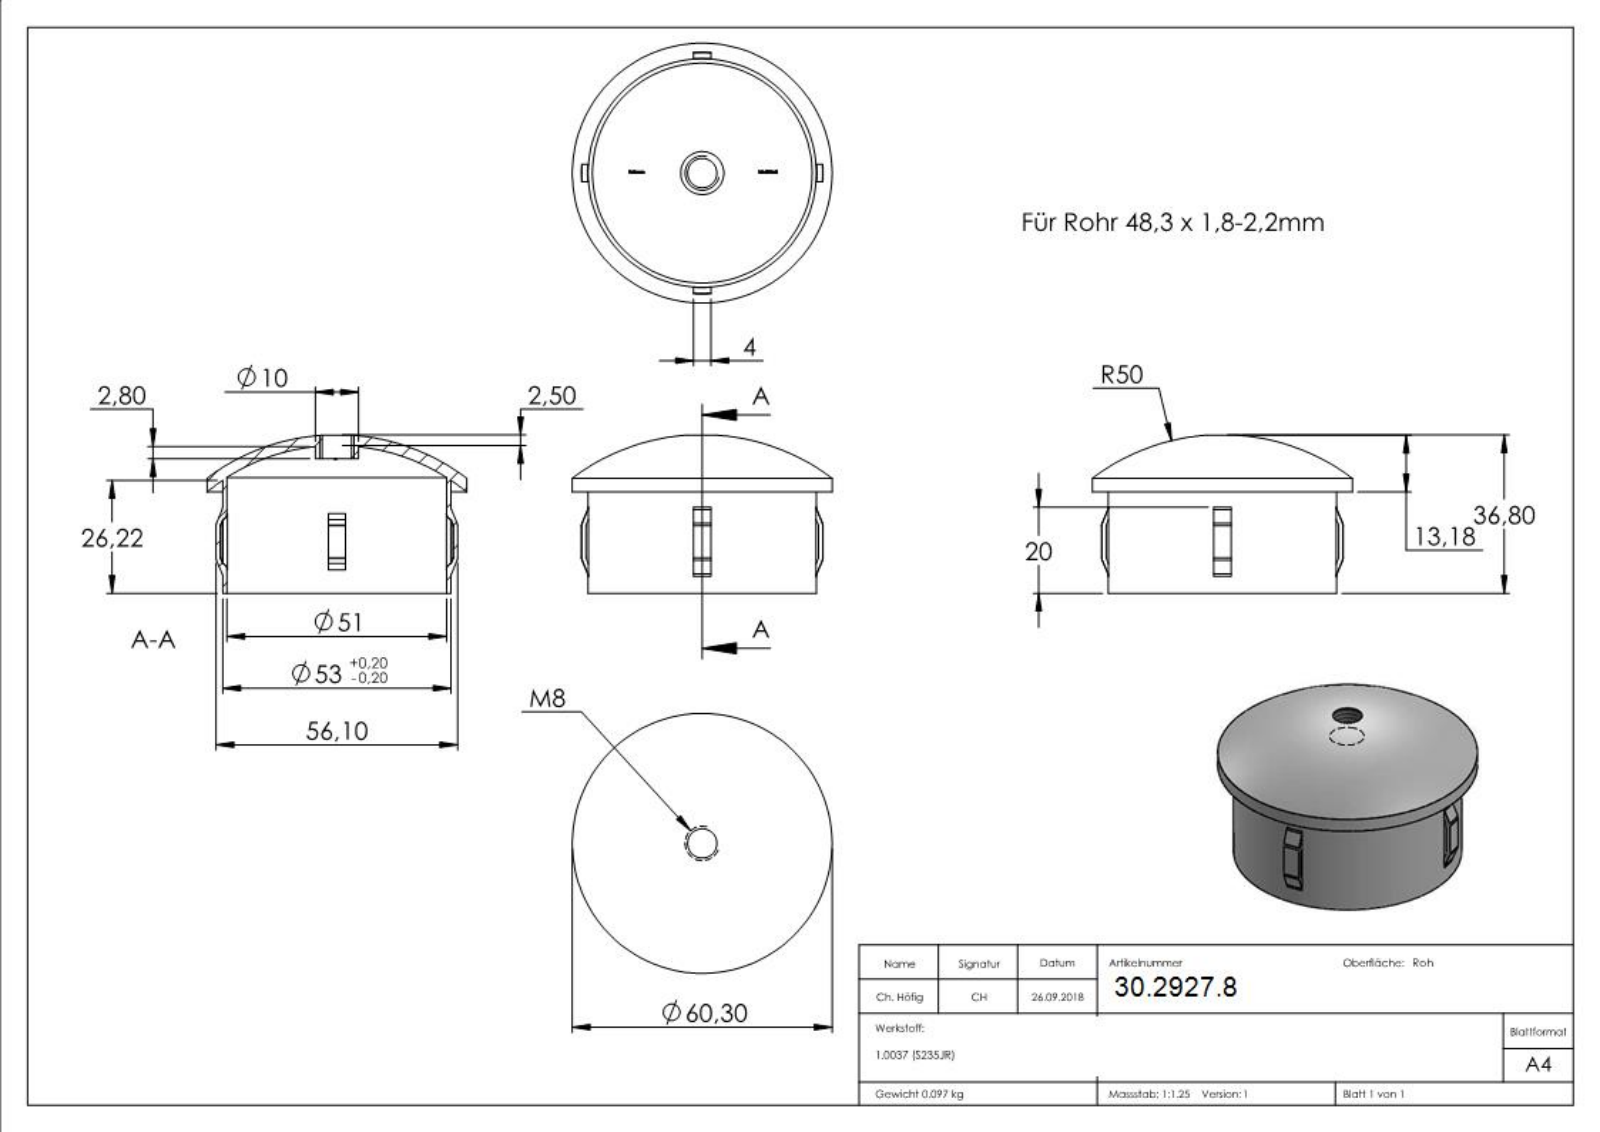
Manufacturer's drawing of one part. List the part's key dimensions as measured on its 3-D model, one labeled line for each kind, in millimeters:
Part name (STEP PRODUCT): 166-6001-M8
STEP written by: SolidWorks 2015 (CONFIG_CONTROL_DESIGN)
Units: millimetres
Bodies: 1 solid, 358 faces (114 planar, 20 cylindrical, 224 other)
Overall size (bounding box): 60.3 × 60.3 × 36.61
Volume: 12 374 mm³ · Surface area: 15 981 mm²
Round holes (diameter × count): ⌀6.8 ×1, ⌀51 ×1
Round bosses / shafts (diameter × count): ⌀60.3 ×1, ⌀53 ×1, ⌀10 ×1
Partial cylindrical surfaces — rounded edges, fillets, slot ends (radius × count): R27.05 ×1, R28.05 ×1
Main face-to-face distances: 4, 31.23, 2, 1.21, 1.78, 0.83, 0.44, 0.99, 32.85, 28.82
